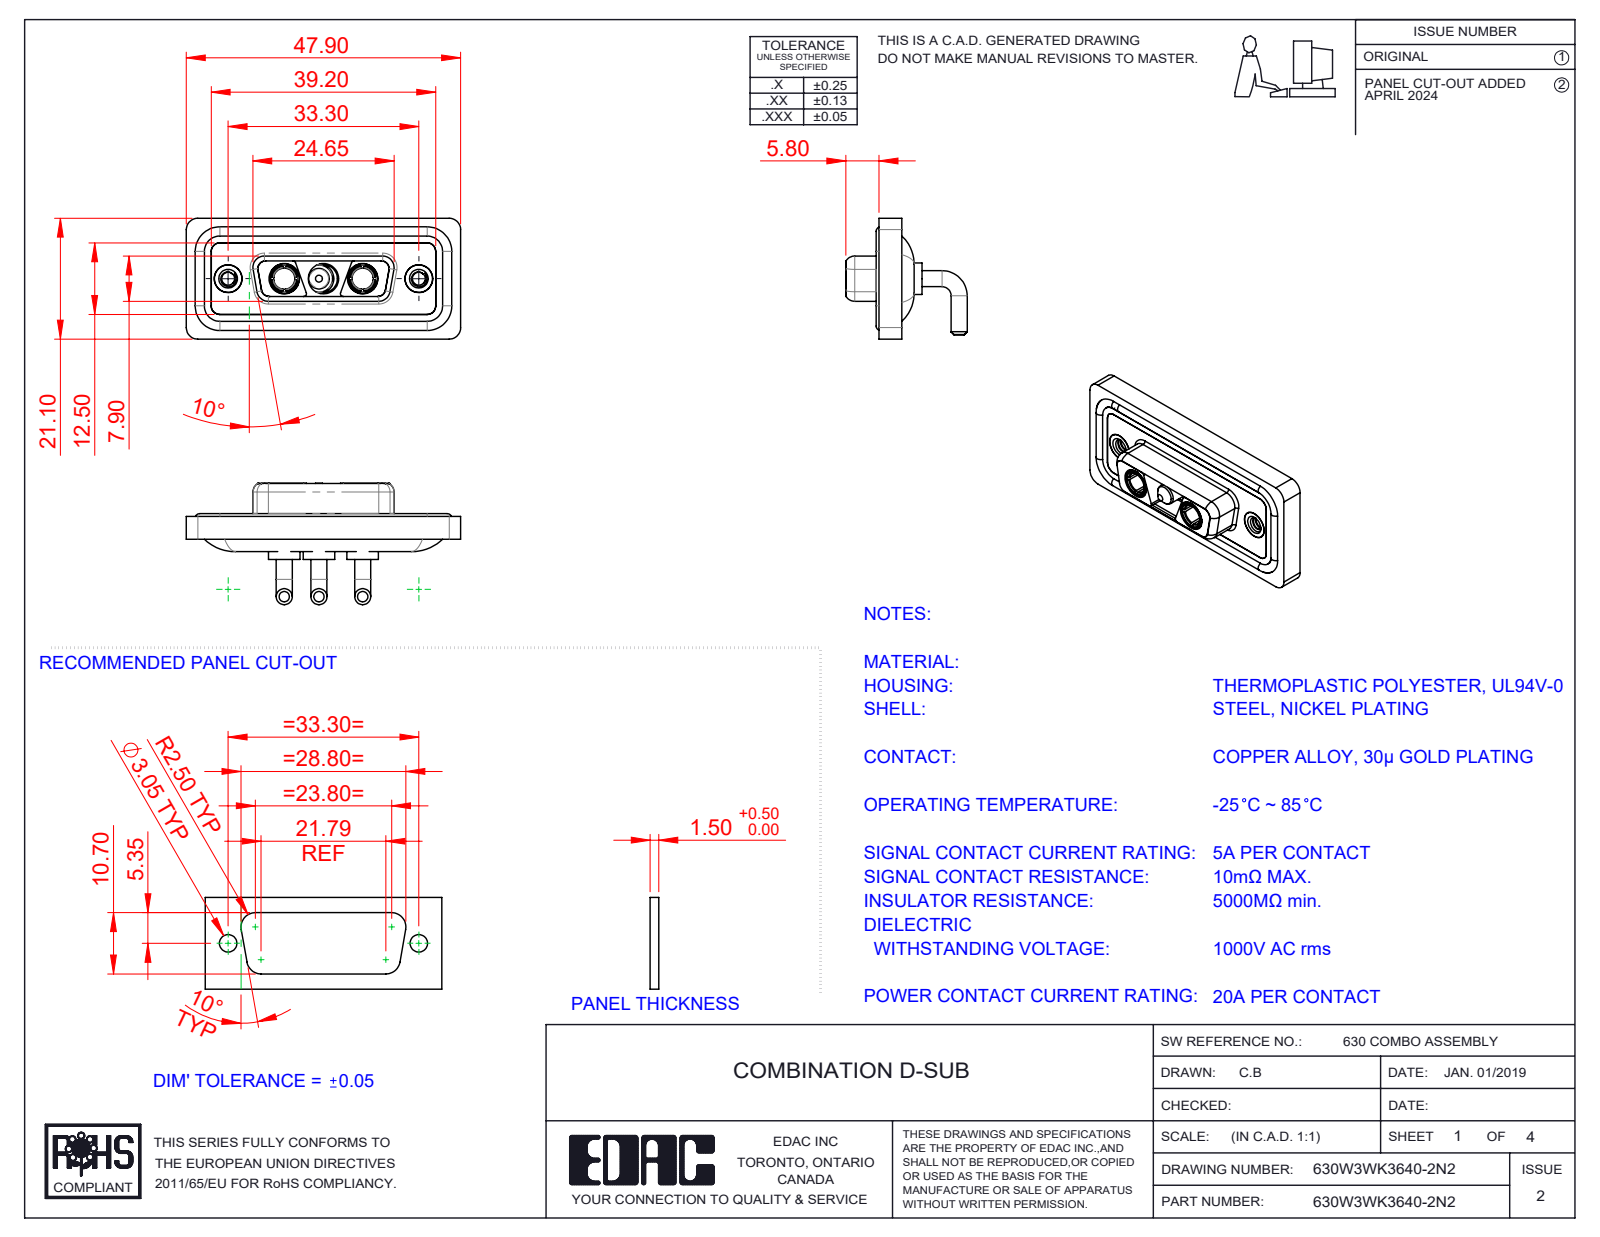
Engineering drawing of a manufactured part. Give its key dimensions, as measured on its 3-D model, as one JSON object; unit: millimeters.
{"part_name": "630Combo Waterproof Housing_15 Contacts; 630Combo Shell Rear_15 Contacts; 630W3WK3640-2N2; 630Combo Housing_3WK3 (+4 more)", "step_written_by": "SolidWorks 2023 (CONFIG_CONTROL_DESIGN)", "units": "millimeters", "bodies": {"solids": 13, "faces": 595, "planar": 178, "cylindrical": 264, "other": 153}, "overall_size": [47.9, 21.2, 21.1], "volume_mm3": 6032, "surface_area_mm2": 9738, "round_holes": [[4.85, 5], [5.3, 3], [2.26, 2], [3.7, 2], [4, 2], [4.05, 2], [5, 2]], "round_bosses_or_shafts": [[2.8, 6], [1.6, 4], [5.5, 3], [5.2, 3], [4.75, 3], [3.75, 3], [4.96, 2], [4.95, 2]], "partial_cylinders_radius": [[2, 20], [1.5, 18], [1.35, 12], [0.5, 8], [1.6, 8], [0.25, 4], [0.6, 4], [0.65, 4]], "face_to_face_distances": [0.4, 1.8, 1.1, 1.6, 2.9, 2.5, 3.1, 3.7, 4.1, 1.5], "hole_center_spacings": [6.85, 9.8, 16.65, 23.5, 13.7, 33.3]}
